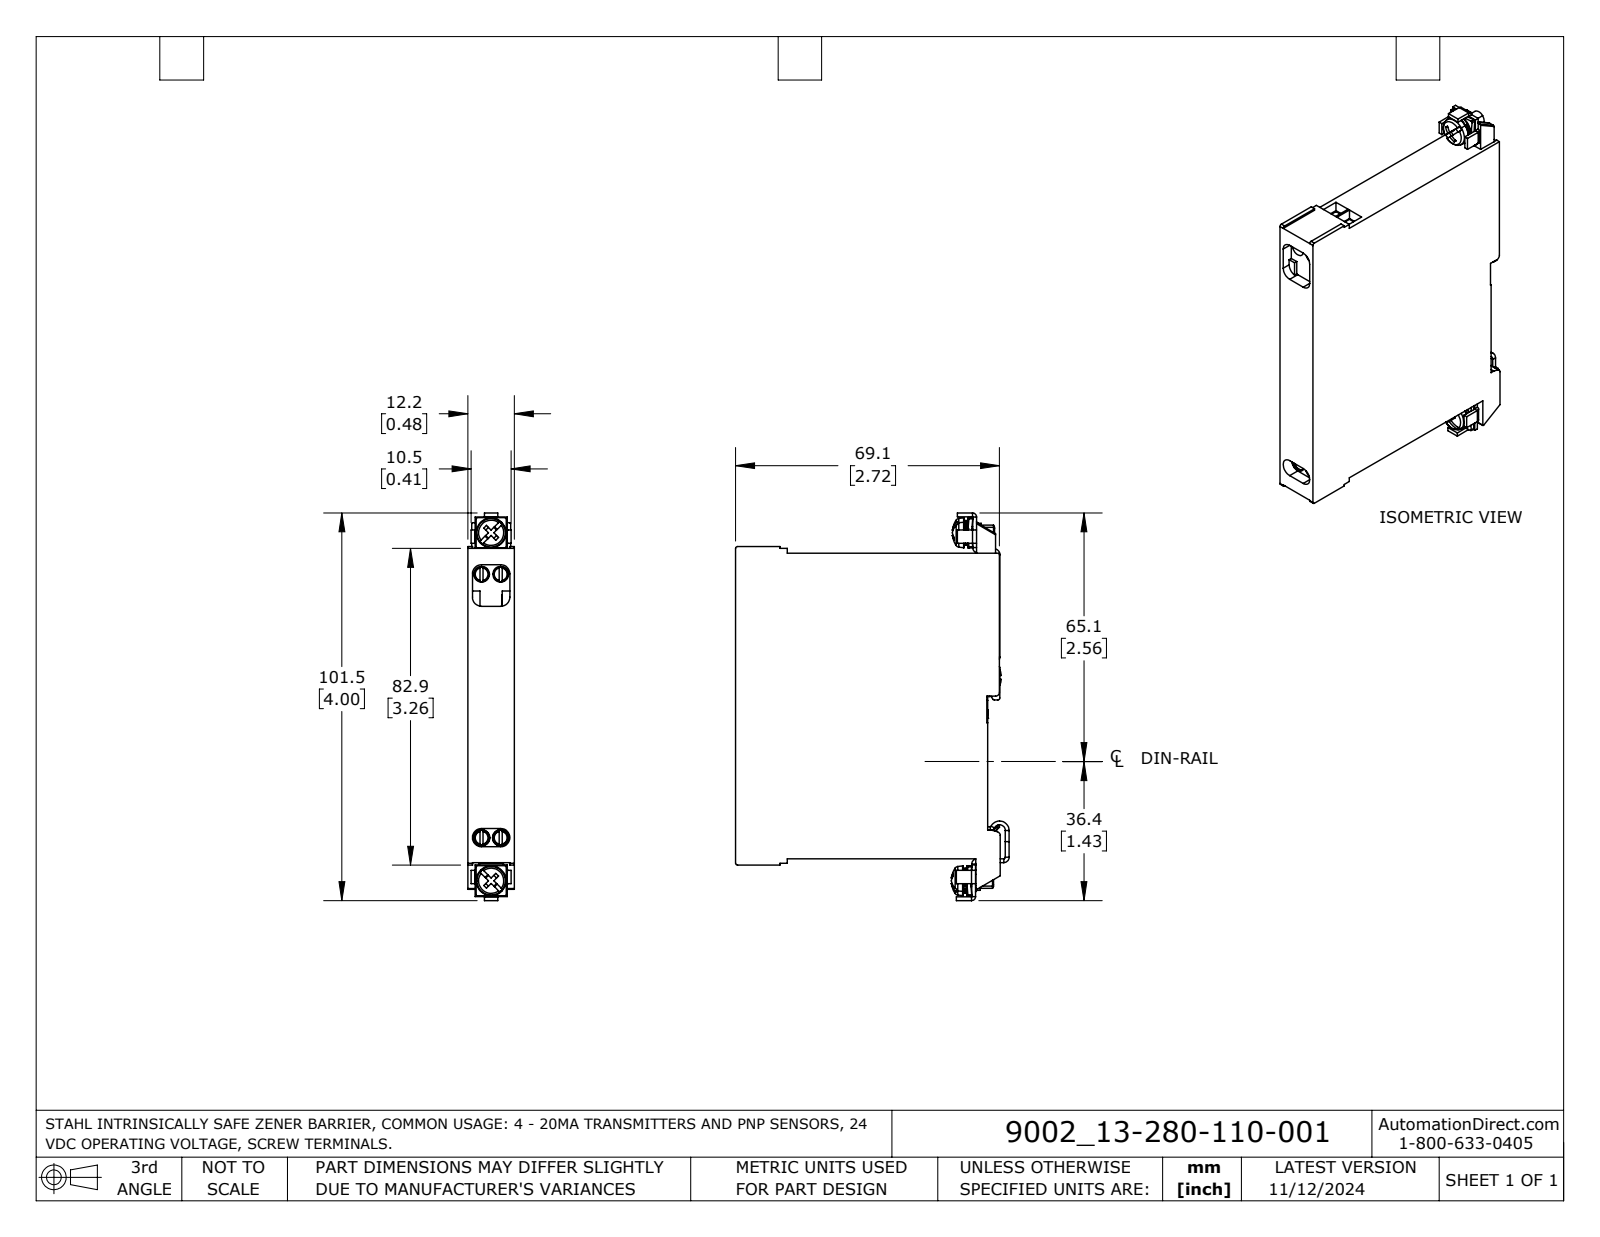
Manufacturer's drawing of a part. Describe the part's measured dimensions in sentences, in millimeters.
The part is named "900213-280-110-001". Its 3-D file was written by "SolidWorks 2023 (AUTOMOTIVE_DESIGN)". It is 4 solids with 762 faces: 528 planar, 146 cylindrical and 88 other. Overall it measures 101.5 by 71.6 by 12.2 millimeters. Its volume is 65 250 cubic millimeters and its surface area 21 750 square millimeters. Round holes: 4 of diameter 4.1, 3 of diameter 4.3, 2 of diameter 3.3, 2 of diameter 4.2, 1 of diameter 3. Round bosses or shafts: 3 of diameter 7.8, 3 of diameter 4, 2 of diameter 5, 2 of diameter 3.1, 1 of diameter 6.5. Partial cylindrical surfaces (rounded edges, fillets, slot ends): 16 of radius 0.5, 8 of radius 0.3, 6 of radius 0.4, 6 of radius 1, 6 of radius 1, 6 of radius 1.4, 6 of radius 2.4, 4 of radius 0.3. The main face-to-face distances are 12.2, 1, 79, 1.1, 2, 78, 2.2, 80, 2.1, 1.2. The hole center spacings are 5, 11.1, 11.5, 27.1, 28.2, 41, 42.1, 69.
